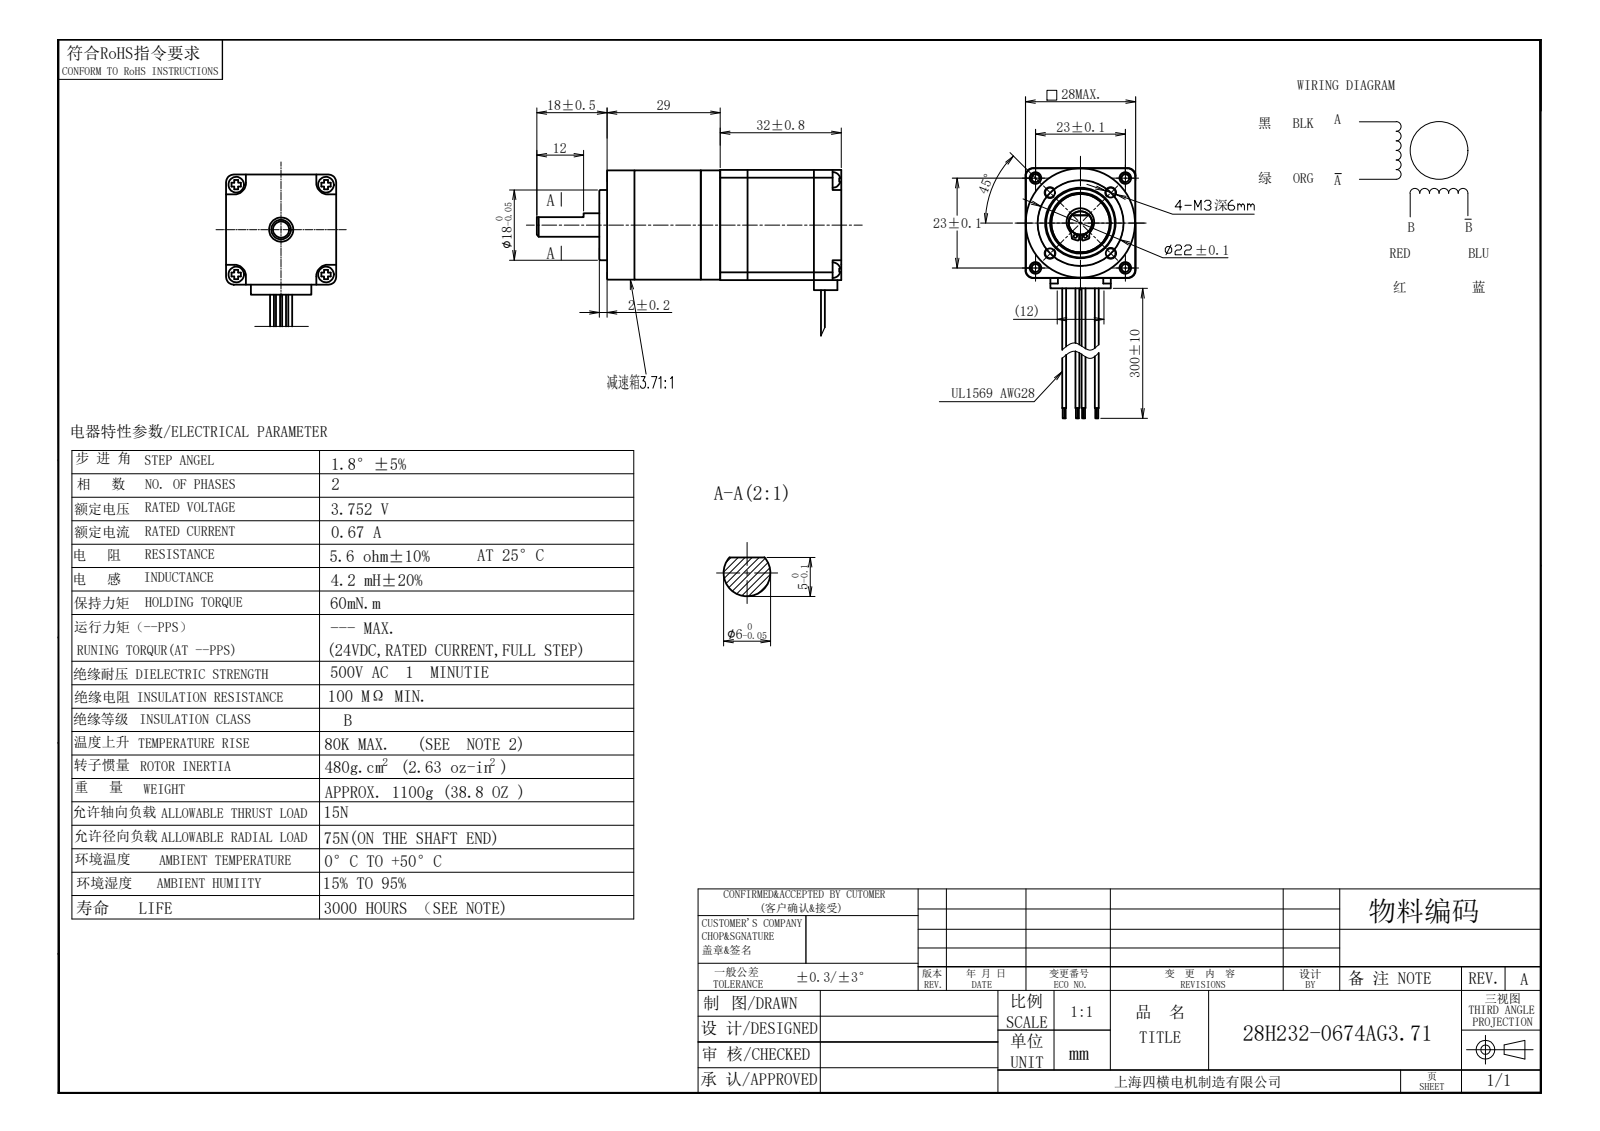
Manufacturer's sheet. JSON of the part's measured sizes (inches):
{"part_name": "Цб; M2.5螺钉; PLA28-003前端盖; 28定子模型 (+8 more)", "step_written_by": "SolidWorks 2020 (CONFIG_CONTROL_DESIGN)", "units": "inches", "bodies": {"solids": 19, "faces": 829, "planar": 168, "cylindrical": 563, "other": 98}, "overall_size": [2.961, 2.165, 1.102], "volume_in3": 2.1, "surface_area_in2": 37.97, "round_holes": [[0.081, 8], [0.118, 7], [0.114, 6], [0.098, 4], [0.047, 2], [0.256, 1], [0.291, 1], [0.295, 1], [0.472, 1], [0.492, 1], [0.512, 1], [0.591, 1]], "round_bosses_or_shafts": [[0.161, 4], [0.098, 4], [0.046, 3], [1.102, 1], [0.866, 1], [0.846, 1], [0.709, 1], [0.673, 1]], "partial_cylinders_radius": [[0.008, 92], [0.11, 92], [0.02, 22], [0.012, 6], [0.039, 4], [0.079, 4], [0.118, 2], [0.187, 1]], "face_to_face_distances": [1.102, 0.276, 0.827, 0.787, 0.551, 1.063, 0.354, 0.079, 0.138, 0.866], "hole_center_spacings": [0.773, 0.207, 0.433, 0.613, 0.64, 0.906, 1.074, 0.309]}
